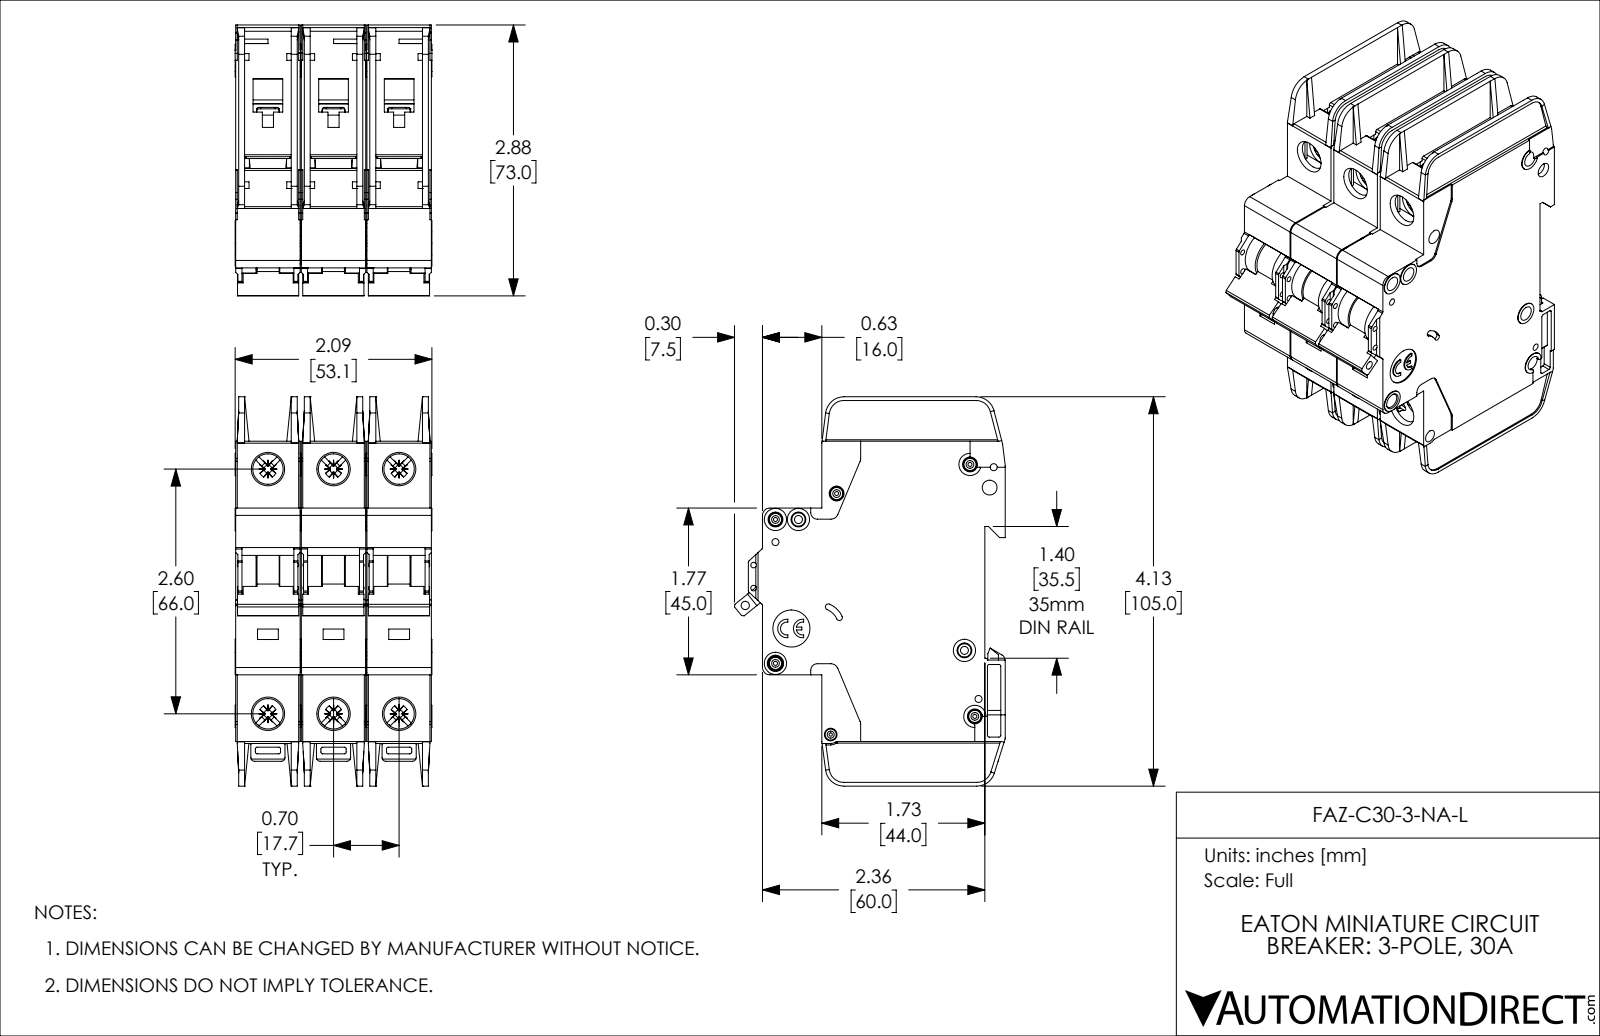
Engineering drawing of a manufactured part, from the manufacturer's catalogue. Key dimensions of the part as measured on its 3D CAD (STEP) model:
Part name (STEP PRODUCT): FAZ-C30-3-NA-L
STEP written by: SolidWorks 2019 (AUTOMOTIVE_DESIGN)
Units: inches
Bodies: 3 solids, 3381 faces (2013 planar, 1071 cylindrical, 297 other)
Overall size (bounding box): 4.134 × 2.876 × 2.091
Volume: 14.05 in³ · Surface area: 123 in²
Round holes (diameter × count): ⌀0.157 ×8, ⌀0.323 ×6, ⌀0.043 ×5, ⌀0.075 ×4, ⌀0.059 ×2, ⌀0.085 ×2, ⌀0.035 ×1, ⌀0.089 ×1, ⌀0.098 ×1, ⌀0.134 ×1, ⌀0.394 ×1
Round bosses / shafts (diameter × count): ⌀0.13 ×5, ⌀0.236 ×4, ⌀0.118 ×4, ⌀0.098 ×3
Partial cylindrical surfaces — rounded edges, fillets, slot ends (radius × count): R0.02 ×72, R0.016 ×30, R0.039 ×18, R0.043 ×12, R0.079 ×12, R0.008 ×6, R0.01 ×6, R0.028 ×6
Main face-to-face distances: 0.697, 0.047, 1.394, 0.685, 0.591, 1.382, 0.744, 0.65, 0.106, 0.094
Hole centre spacings: 0.697, 2.69, 2.598, 0.244, 0.537, 0.87, 1.394, 2.948
